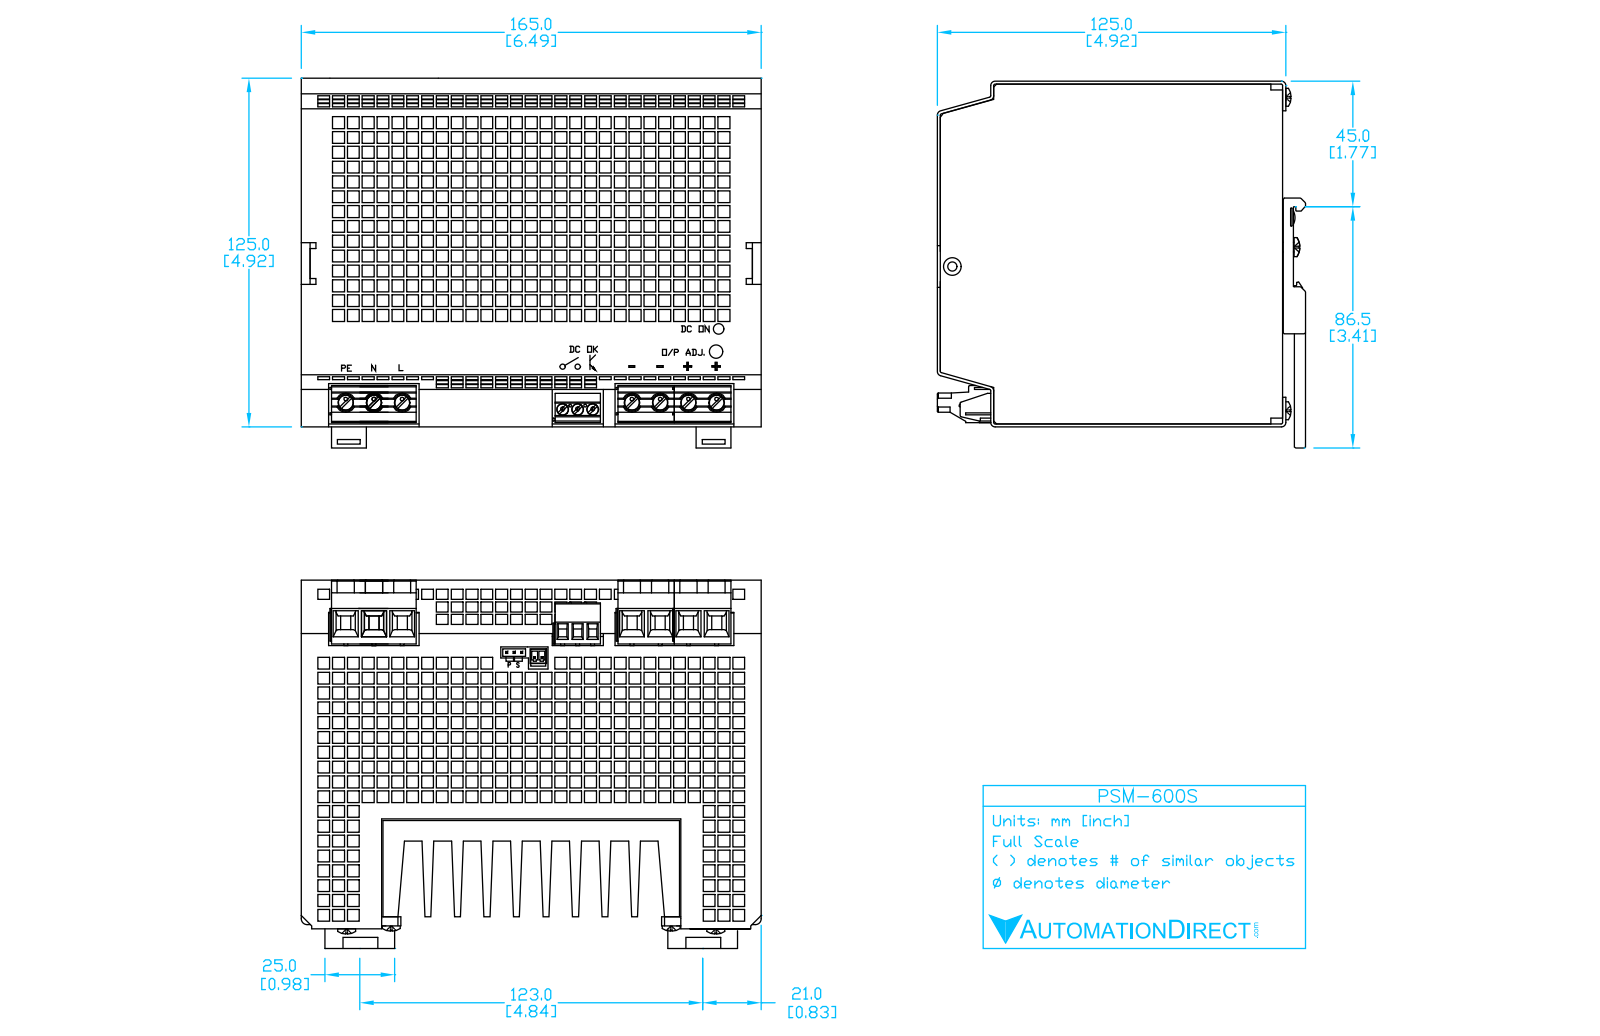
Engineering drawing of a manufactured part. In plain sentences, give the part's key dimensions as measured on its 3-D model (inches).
The part is named "PSM12-156S". Its 3-D file was written by "SolidWorks 2011 (CONFIG_CONTROL_DESIGN)". It is 1 solid with 2327 faces: 2182 planar, 64 cylindrical and 81 other. Overall it measures 4.692 by 4.691 by 2.13 inches. Its volume is 38.63 cubic inches and its surface area 94.73 square inches. Round holes: 10 of diameter 0.16, 1 of diameter 0.15, 1 of diameter 0.172. Round bosses or shafts: 2 of diameter 0.21, 1 of diameter 0.265, 1 of diameter 0.109, 1 of diameter 0.041, 1 of diameter 0.041. Partial cylindrical surfaces (rounded edges, fillets, slot ends): 8 of radius 0.06, 4 of radius 0.02, 2 of radius 0.03, 2 of radius 0.07, 2 of radius 0.081. The main face-to-face distances are 2.128, 0.04, 4.29, 4.33, 4.291, 4.25, 0.02, 0.04, 0.572, 1.557. The hole center spacings are 0.2, 0.4, 0.6, 0.8, 0.31, 1, 1.298, 3.88.
